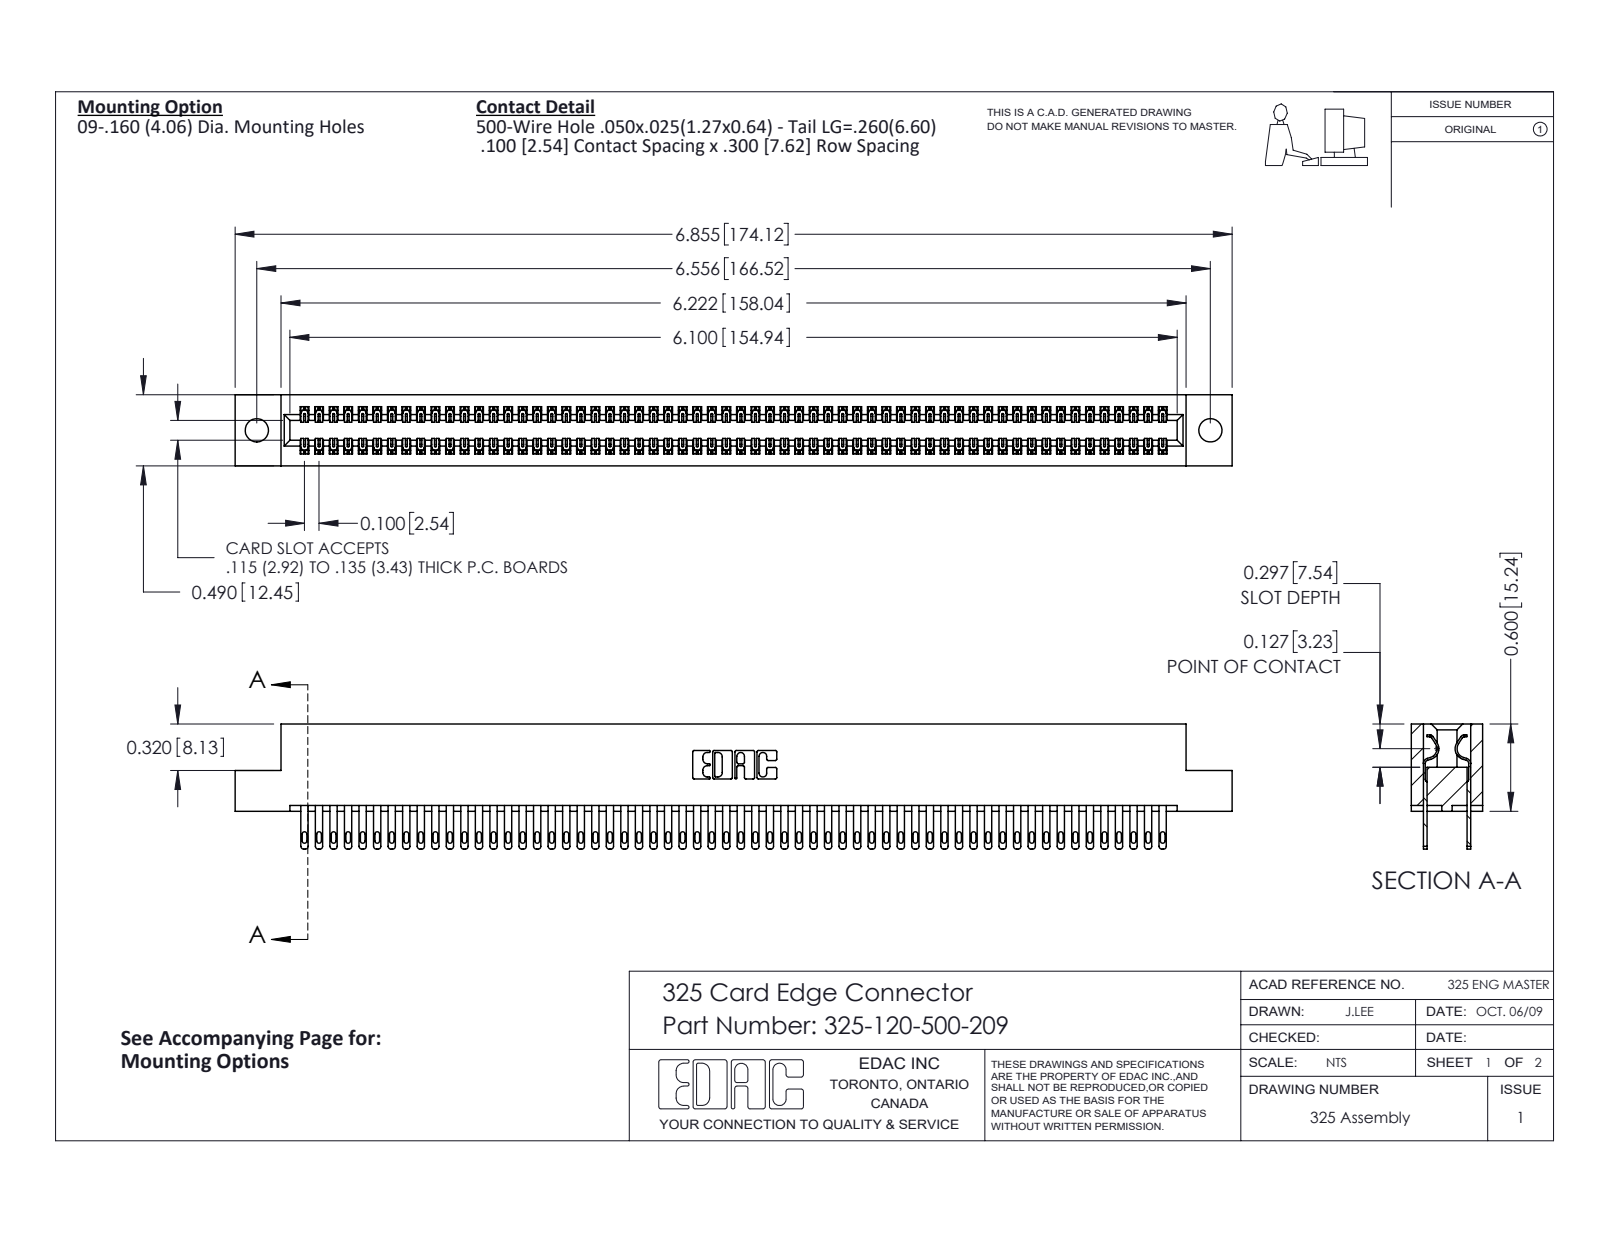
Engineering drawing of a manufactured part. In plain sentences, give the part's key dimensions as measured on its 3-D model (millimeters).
The part is named "325-292-001_325-293-100; 325 Part_.160 TH; 325-120-500-209". Its 3-D file was written by "SolidWorks 2016 (CONFIG_CONTROL_DESIGN)". It is 121 solids with 5874 faces: 3670 planar, 2204 cylindrical and 0 other. Overall it measures 174.1 by 21.8 by 12.4 millimeters. Its volume is 22 780 cubic millimeters and its surface area 29 170 square millimeters. Round holes: 2 of diameter 4.1. Partial cylindrical surfaces (rounded edges, fillets, slot ends): 180 of radius 0.2, 120 of radius 0.4, 120 of radius 0.5, 22 of radius 0.3, 6 of radius 0.2, 6 of radius 0.8, 3 of radius 0.7, 2 of radius 0.4. The main face-to-face distances are 2.1, 10.3, 7.6, 2.7, 9.7, 0.6, 8.3, 12.4, 7, 14.2. The hole center spacings are 166.5.
